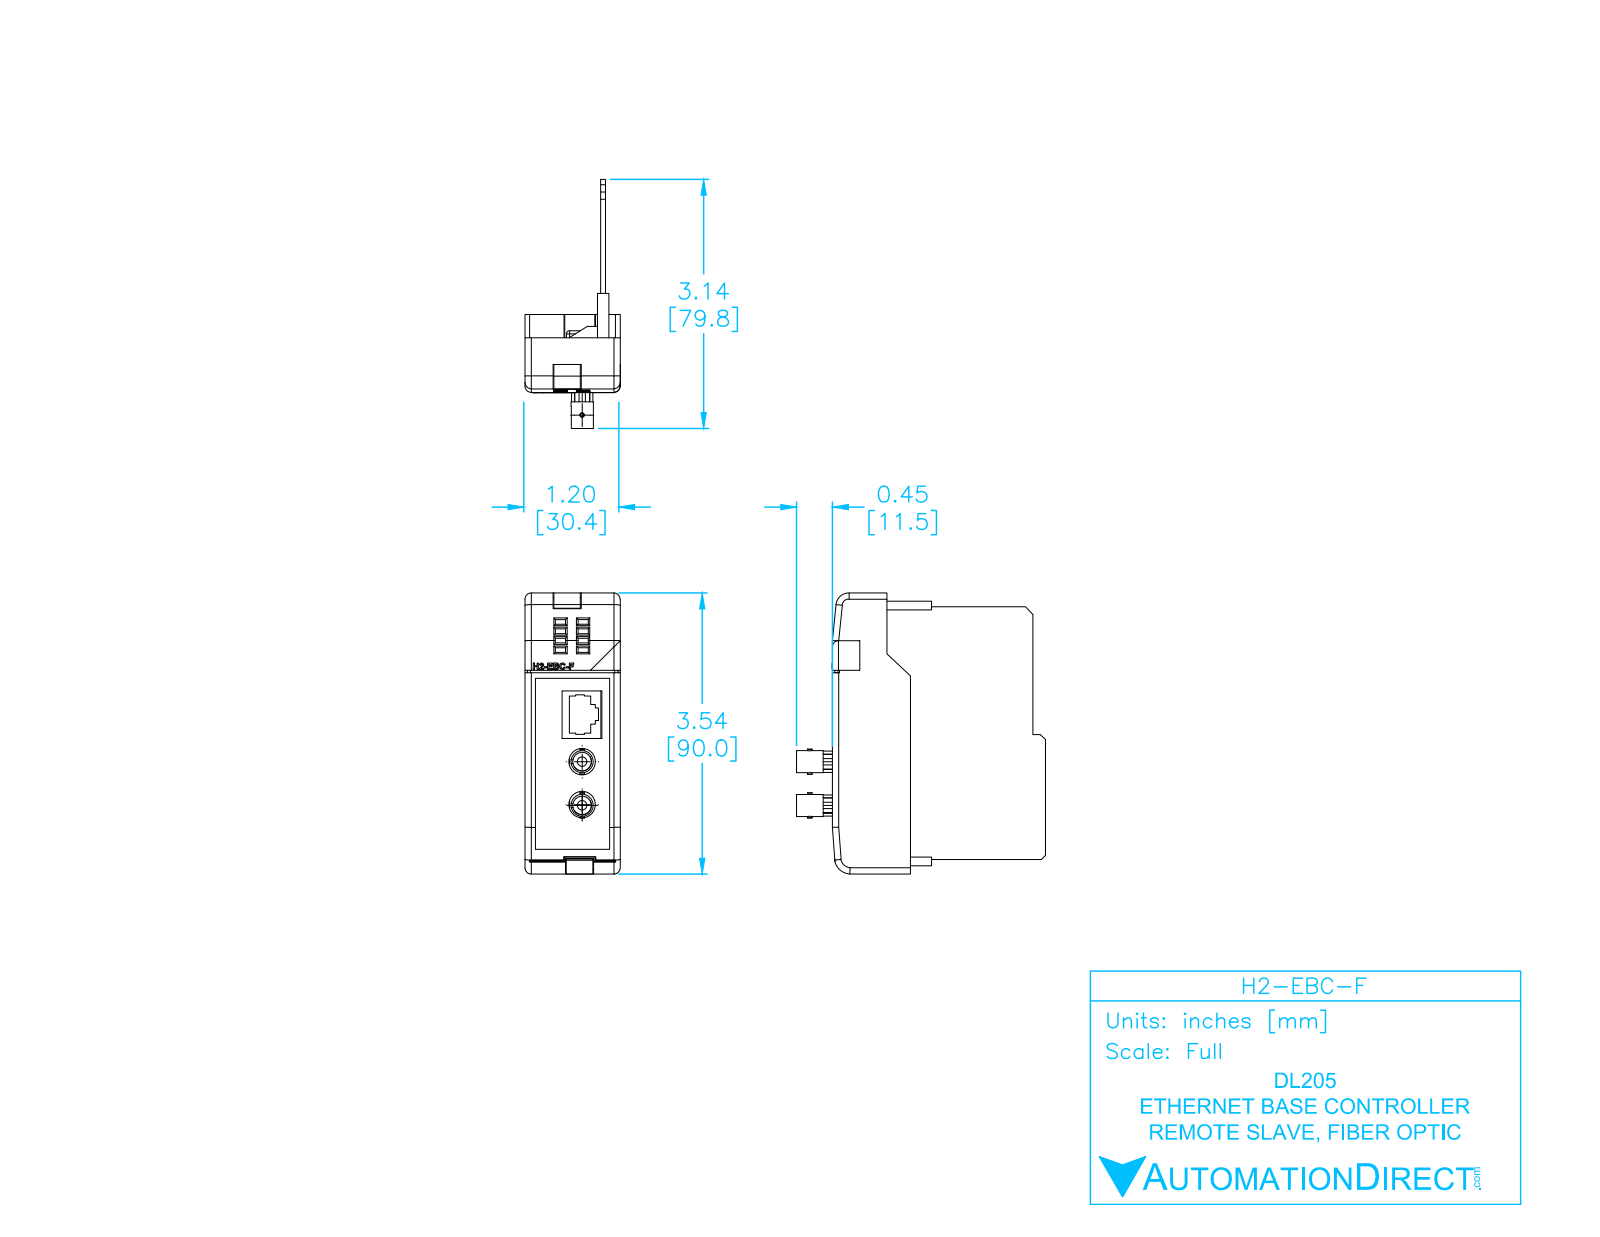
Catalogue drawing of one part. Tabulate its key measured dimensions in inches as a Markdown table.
| quantity | value |
| --- | --- |
| part name | H2-EBC-F |
| STEP written by | SolidWorks 2009 (AUTOMOTIVE_DESIGN) |
| units | inches |
| bodies | 5 solids, 504 faces (323 planar, 121 cylindrical, 60 other) |
| overall size | 3.543 × 3.141 × 1.203 |
| volume | 1.516 in³ |
| surface area | 49.18 in² |
| round holes (diameter × count) | 0.118 × 2, 0.236 × 2, 0.335 × 2 |
| round bosses / shafts (diameter × count) | 0.279 × 2, 0.055 × 1 |
| partial cylindrical surfaces (radius × count) | 0.02 × 29, 0.039 × 14, 0.079 × 11, 0.01 × 4, 0.103 × 1, 0.149 × 1, 0.162 × 1, 0.208 × 1 |
| main face-to-face distances | 0.059, 0.186, 0.127, 0.245, 0.02, 1.142, 0.956, 1.083, 1.015, 1.201 |
| hole center spacings | 0.551, 0.541, 0.543, 0.55, 0.553 |
